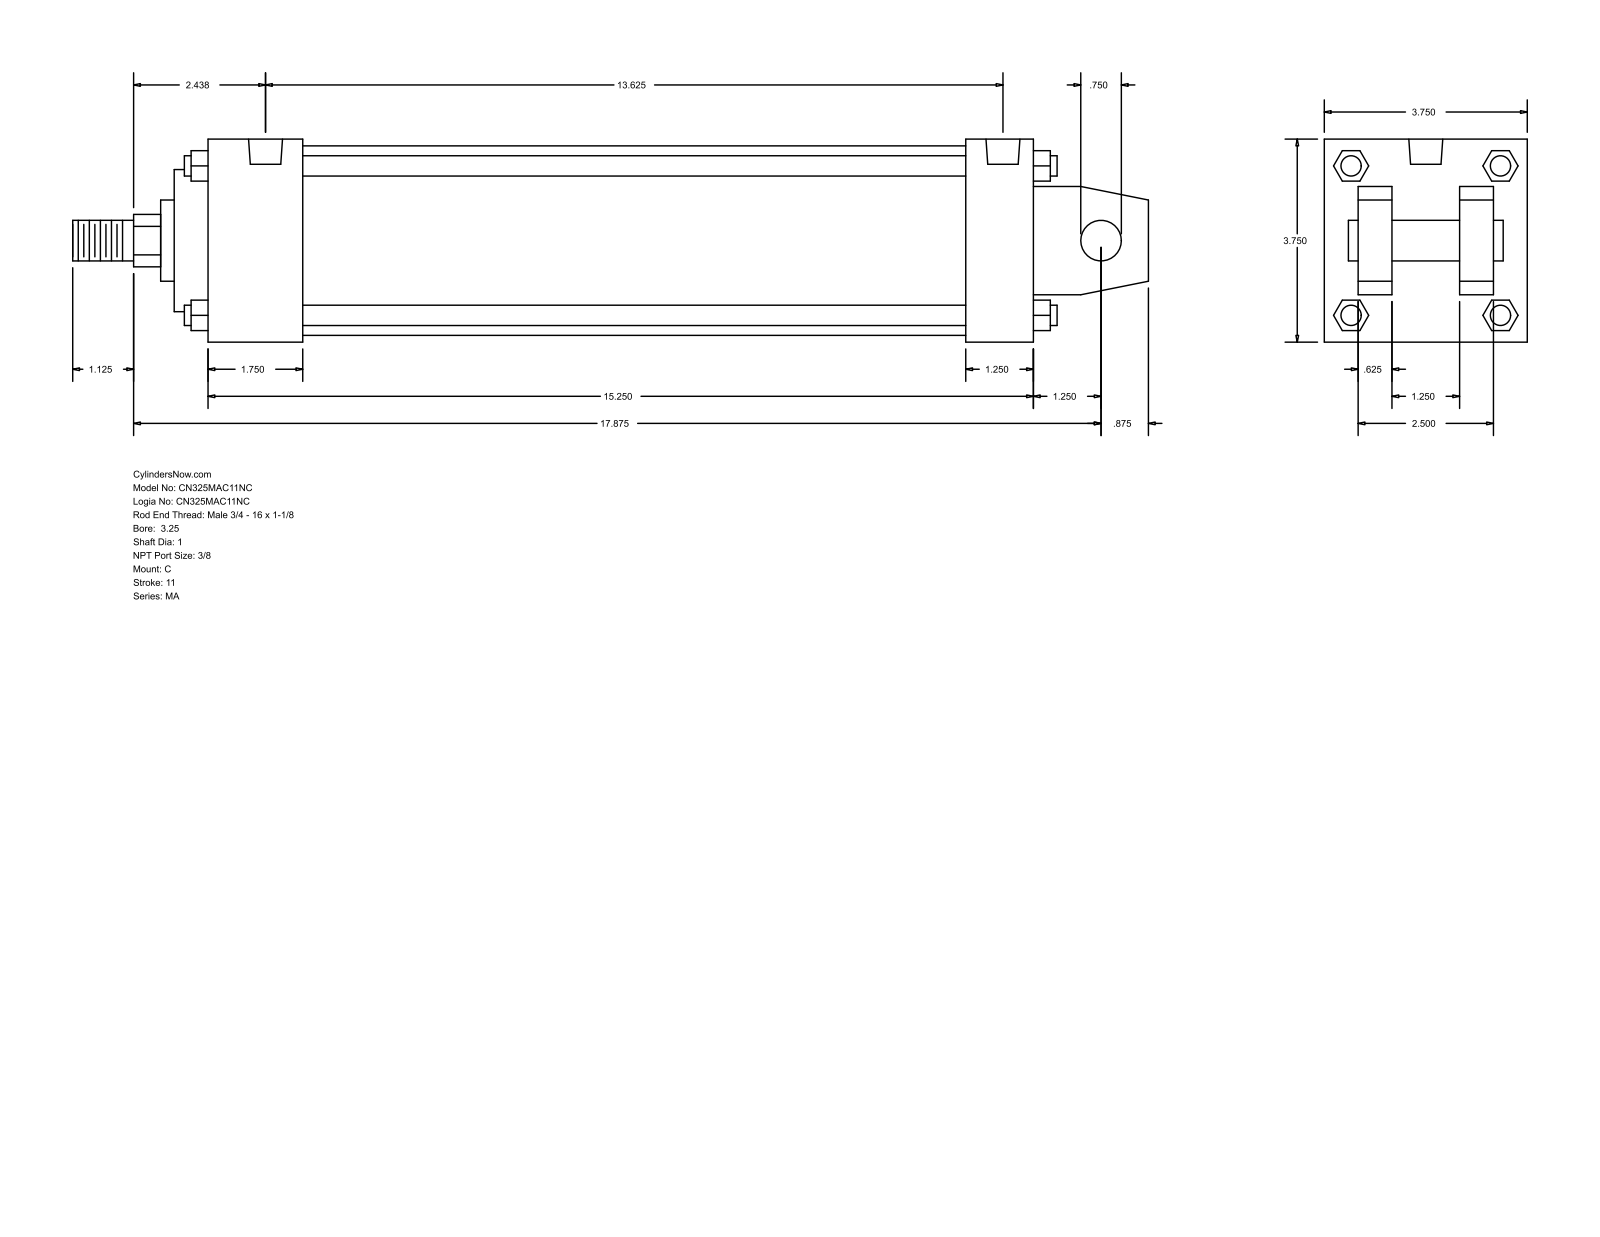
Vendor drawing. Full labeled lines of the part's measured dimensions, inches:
Part name (STEP PRODUCT): MA_C__0325_1
STEP written by: GSSL Pune (CONFIG_CONTROL_DESIGN)
Units: inches
Bodies: 0 solids, 141 faces (109 planar, 32 cylindrical, 0 other)
Overall size (bounding box): 19.875 × 3.75 × 3.75
Round holes (diameter × count): ⌀0.437 ×4, ⌀0.627 ×2
Round bosses / shafts (diameter × count): ⌀0.375 ×4, ⌀0.75 ×2, ⌀3.5 ×1, ⌀2.625 ×1, ⌀1.5 ×1, ⌀1 ×1
Partial cylindrical surfaces — rounded edges, fillets, slot ends (radius × count): R0.484 ×1
Main face-to-face distances: 3.75, 0.625, 2.5, 15.25, 1.25, 3.125, 1.875, 15.875, 14, 1.25
Hole centre spacings: 0.187, 13.25, 13.438, 13.625
